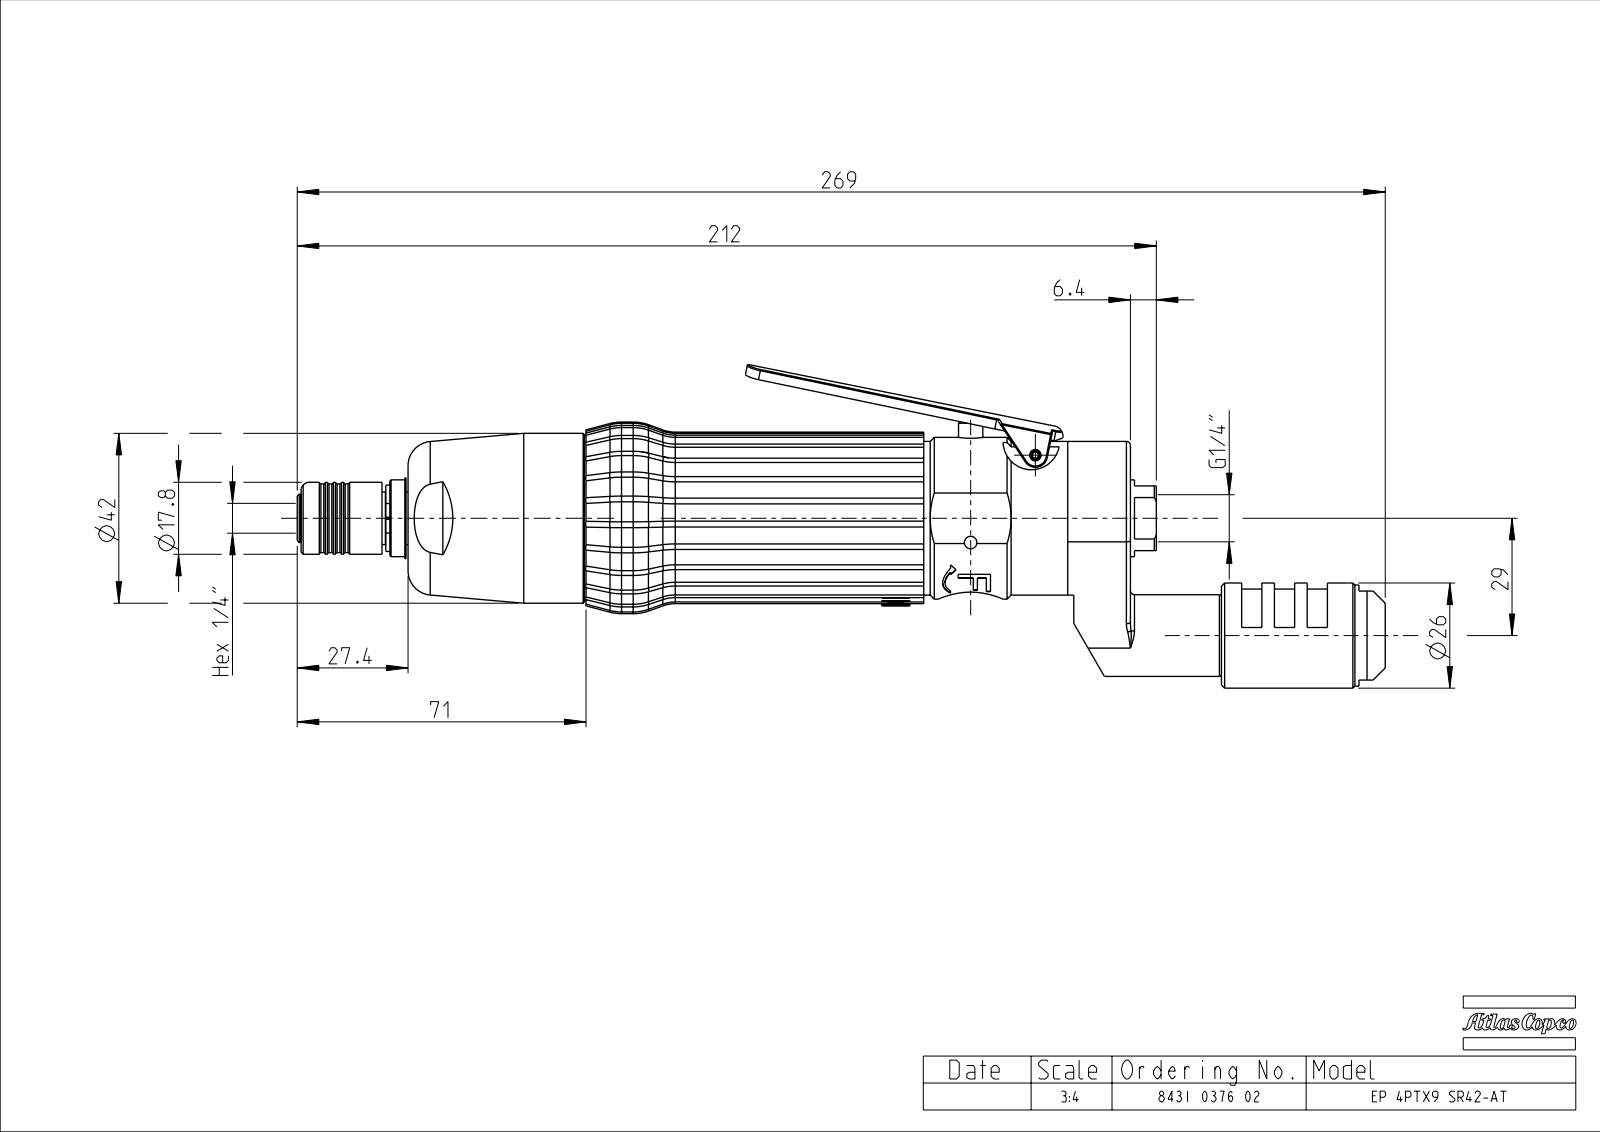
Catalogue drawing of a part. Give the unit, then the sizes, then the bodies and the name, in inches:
Units: inches
Overall size (bounding box): 10.6 × 2.378 × 2.174
Round holes (diameter × count): ⌀0.067 ×2, ⌀0.059 ×1, ⌀0.11 ×1, ⌀0.122 ×1, ⌀0.185 ×1, ⌀0.386 ×1, ⌀0.459 ×1, ⌀0.488 ×1, ⌀0.61 ×1, ⌀0.724 ×1
Round bosses / shafts (diameter × count): ⌀0.591 ×2, ⌀1.654 ×1, ⌀1.575 ×1, ⌀1.496 ×1, ⌀1.024 ×1, ⌀0.984 ×1, ⌀0.906 ×1, ⌀0.795 ×1
Partial cylindrical surfaces — rounded edges, fillets, slot ends (radius × count): R0.039 ×97, R0.02 ×6, R0.138 ×6, R0.012 ×4, R0.157 ×2, R0.118 ×1, R0.128 ×1, R0.236 ×1
Main face-to-face distances: 7.031, 0.039, 0.079, 1.594, 3.043, 1.496, 0.551, 1.417, 2.492, 9.524
Hole centre spacings: 0.32, 0.154, 0.866, 0.987, 1.058, 1.142
Volume: 16.63 in³ · Surface area: 68.06 in²
Bodies: 2 solids, 874 faces (185 planar, 283 cylindrical, 406 other)
Part name (STEP PRODUCT): EXT_COMP_SW0015
STEP written by: CREO PARAMETRIC BY PTC INC, 2020281 (CONFIG_CONTROL_DESIGN)
